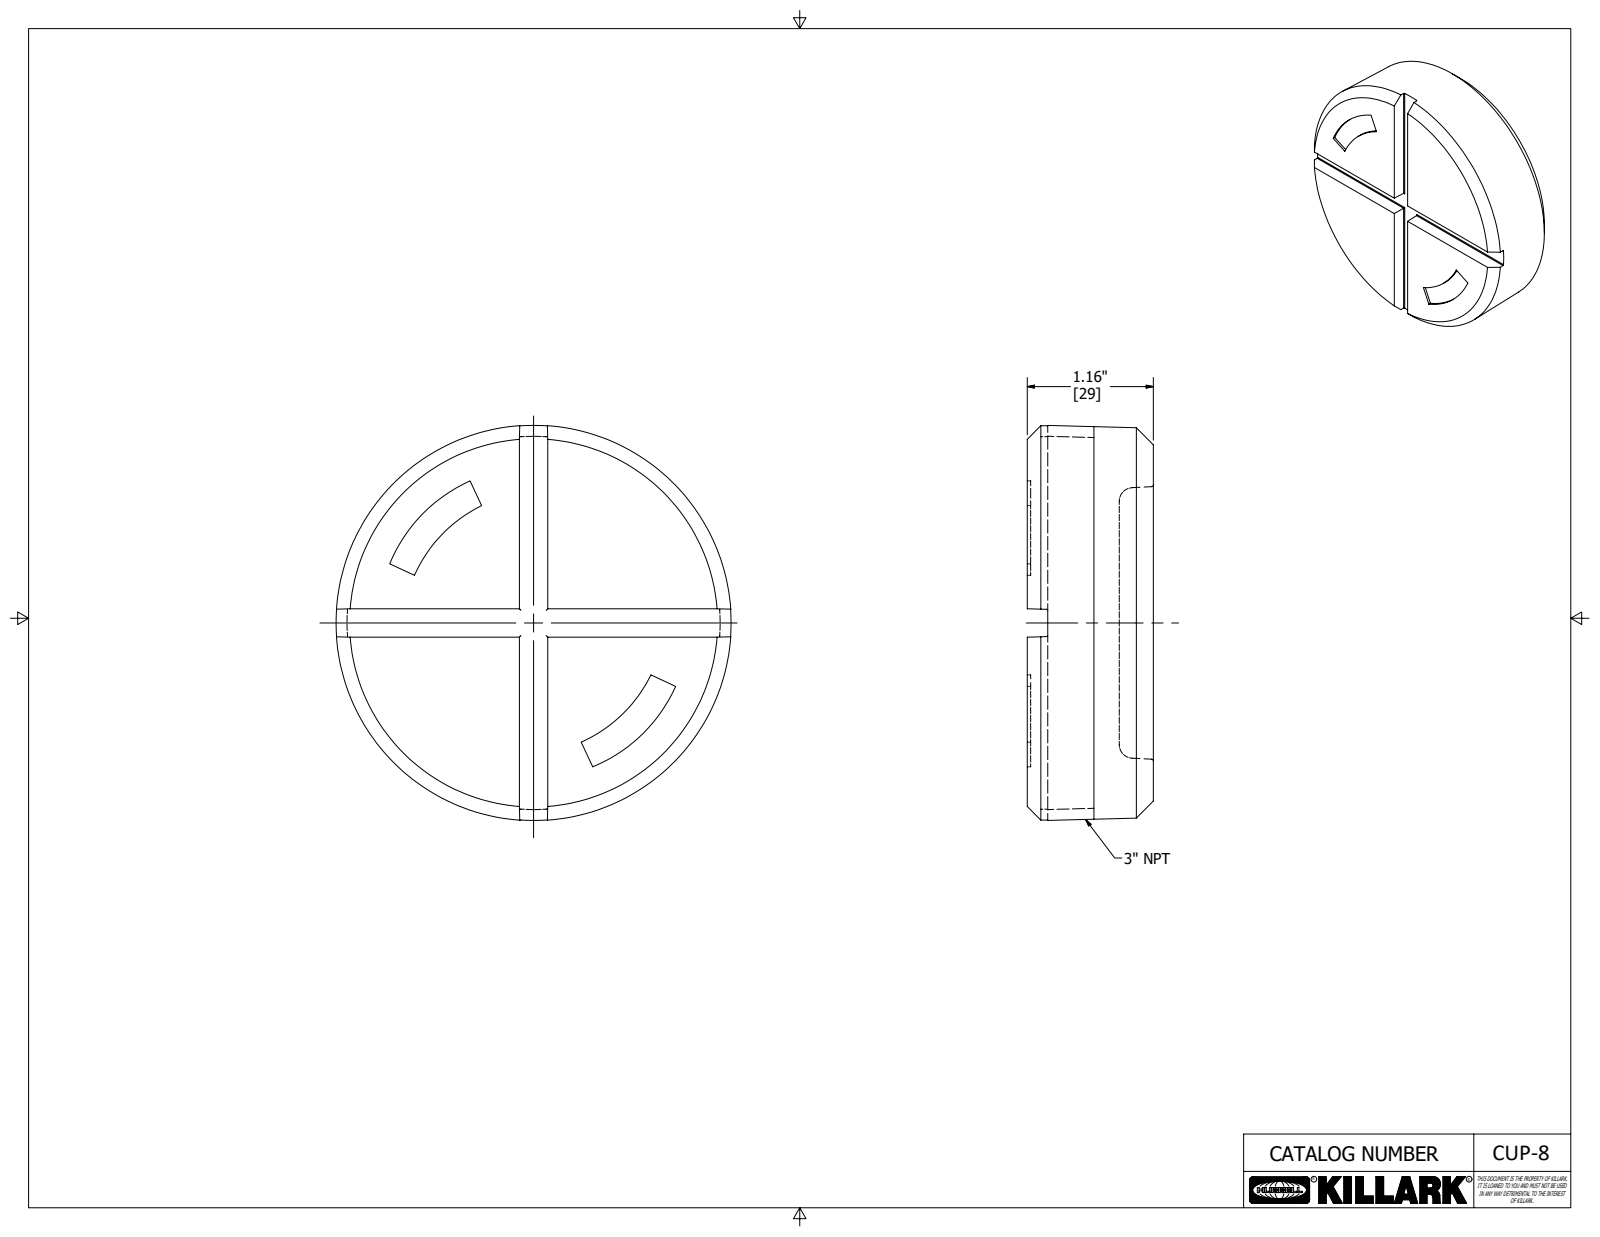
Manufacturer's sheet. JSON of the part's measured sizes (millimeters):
{"part_name": "CUP-8_ETO", "step_written_by": "Autodesk Inventor 2020 (AUTOMOTIVE_DESIGN)", "units": "millimeters", "bodies": {"solids": 1, "faces": 42, "planar": 21, "cylindrical": 12, "other": 9}, "overall_size": [91.99, 91.99, 29.37], "volume_mm3": 159303, "surface_area_mm2": 23106, "partial_cylinders_radius": [[0.25, 4], [32.94, 2], [36.23, 1]], "face_to_face_distances": [21.43, 7.94, 29.37, 24.61, 16.67, 4.76, 28.58, 20.64, 3.97, 0.79]}
